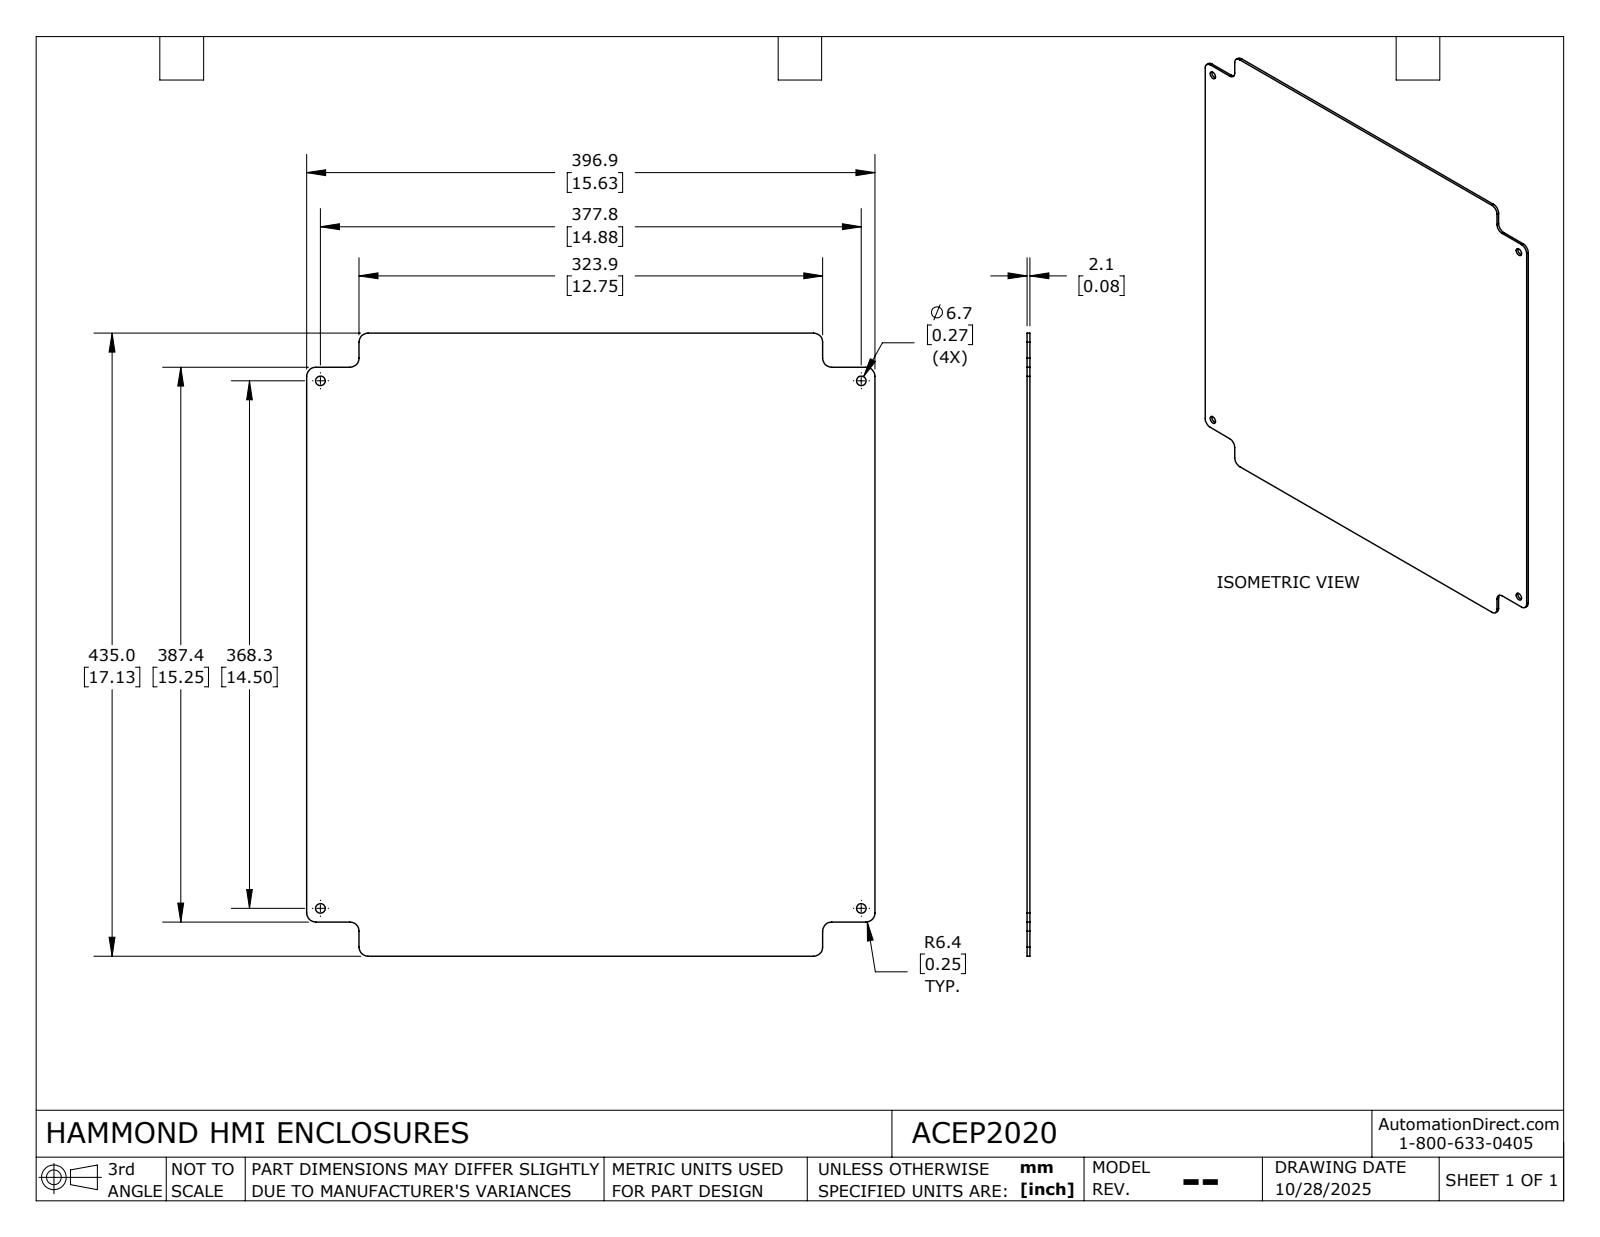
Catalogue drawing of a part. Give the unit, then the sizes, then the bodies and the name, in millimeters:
Units: millimetres
Overall size (bounding box): 434.98 × 396.88 × 2.06
Round holes (diameter × count): ⌀6.73 ×4
Partial cylindrical surfaces — rounded edges, fillets, slot ends (radius × count): R6.35 ×12
Main face-to-face distances: 2.06, 396.88, 434.98, 23.81, 411.17, 387.36, 36.51, 360.37, 323.86
Hole centre spacings: 368.3, 377.82, 527.63
Volume: 347 651 mm³ · Surface area: 341 482 mm²
Bodies: 1 solid, 30 faces (14 planar, 16 cylindrical, 0 other)
Part name (STEP PRODUCT): ACEP2020
STEP written by: SolidWorks 2024 (AUTOMOTIVE_DESIGN)
